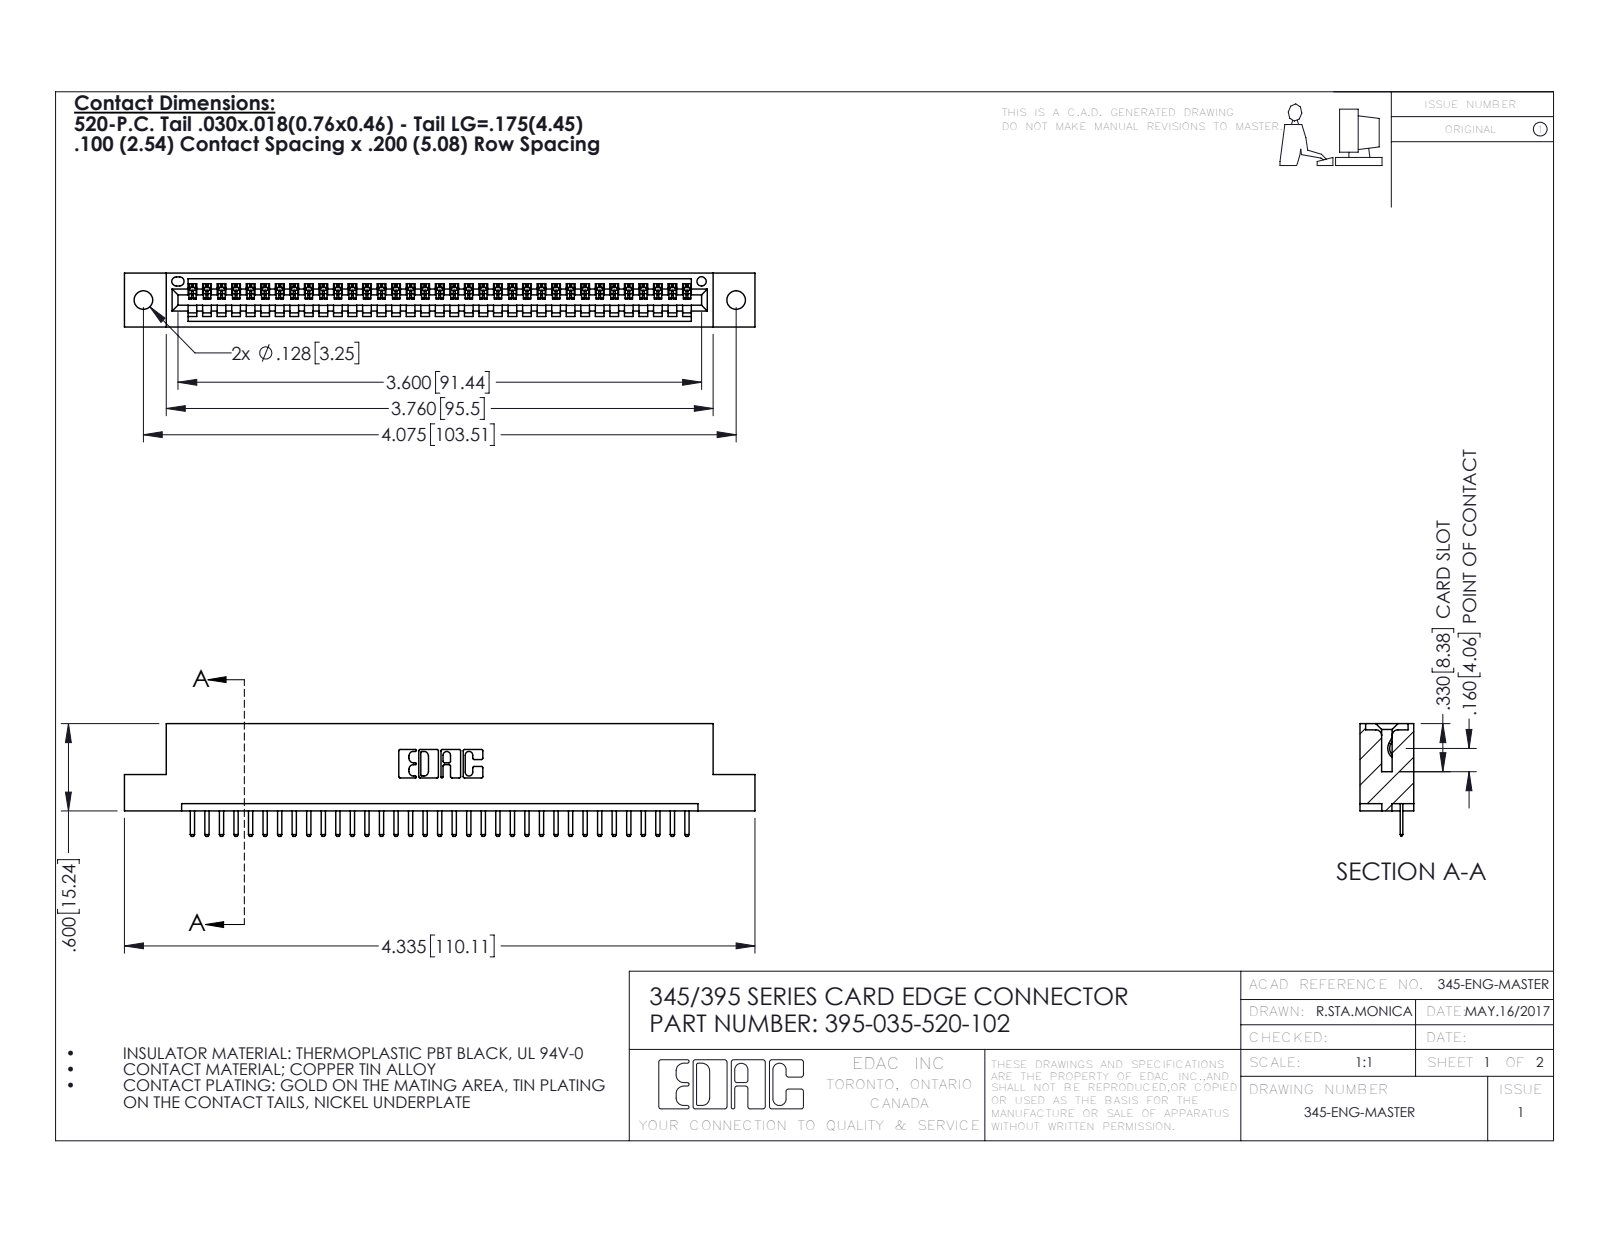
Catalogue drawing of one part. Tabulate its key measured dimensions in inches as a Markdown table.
| quantity | value |
| --- | --- |
| part name | 345 Part_Flush Mounting Lugs - 0.128 Dia; 395-035-520-102; 345-292-001_345-293-120 |
| STEP written by | SolidWorks 2016 (CONFIG_CONTROL_DESIGN) |
| units | inches |
| bodies | 36 solids, 2296 faces (1550 planar, 746 cylindrical, 0 other) |
| overall size | 4.335 × 0.775 × 0.37 |
| volume | 0.626 in³ |
| surface area | 20.06 in² |
| round holes (diameter × count) | 0.128 × 2, 0.064 × 1 |
| partial cylindrical surfaces (radius × count) | 0.01 × 72, 0.006 × 70, 0.01 × 22, 0.007 × 6, 0.031 × 6, 0.026 × 3, 0.031 × 2, 0.04 × 2 |
| main face-to-face distances | 0.298, 0.072, 0.37, 0.2, 0.098, 0.272, 0.025, 0.225, 0.072, 0.149 |
| hole center spacings | 0.27, 3.839, 4.075 |
